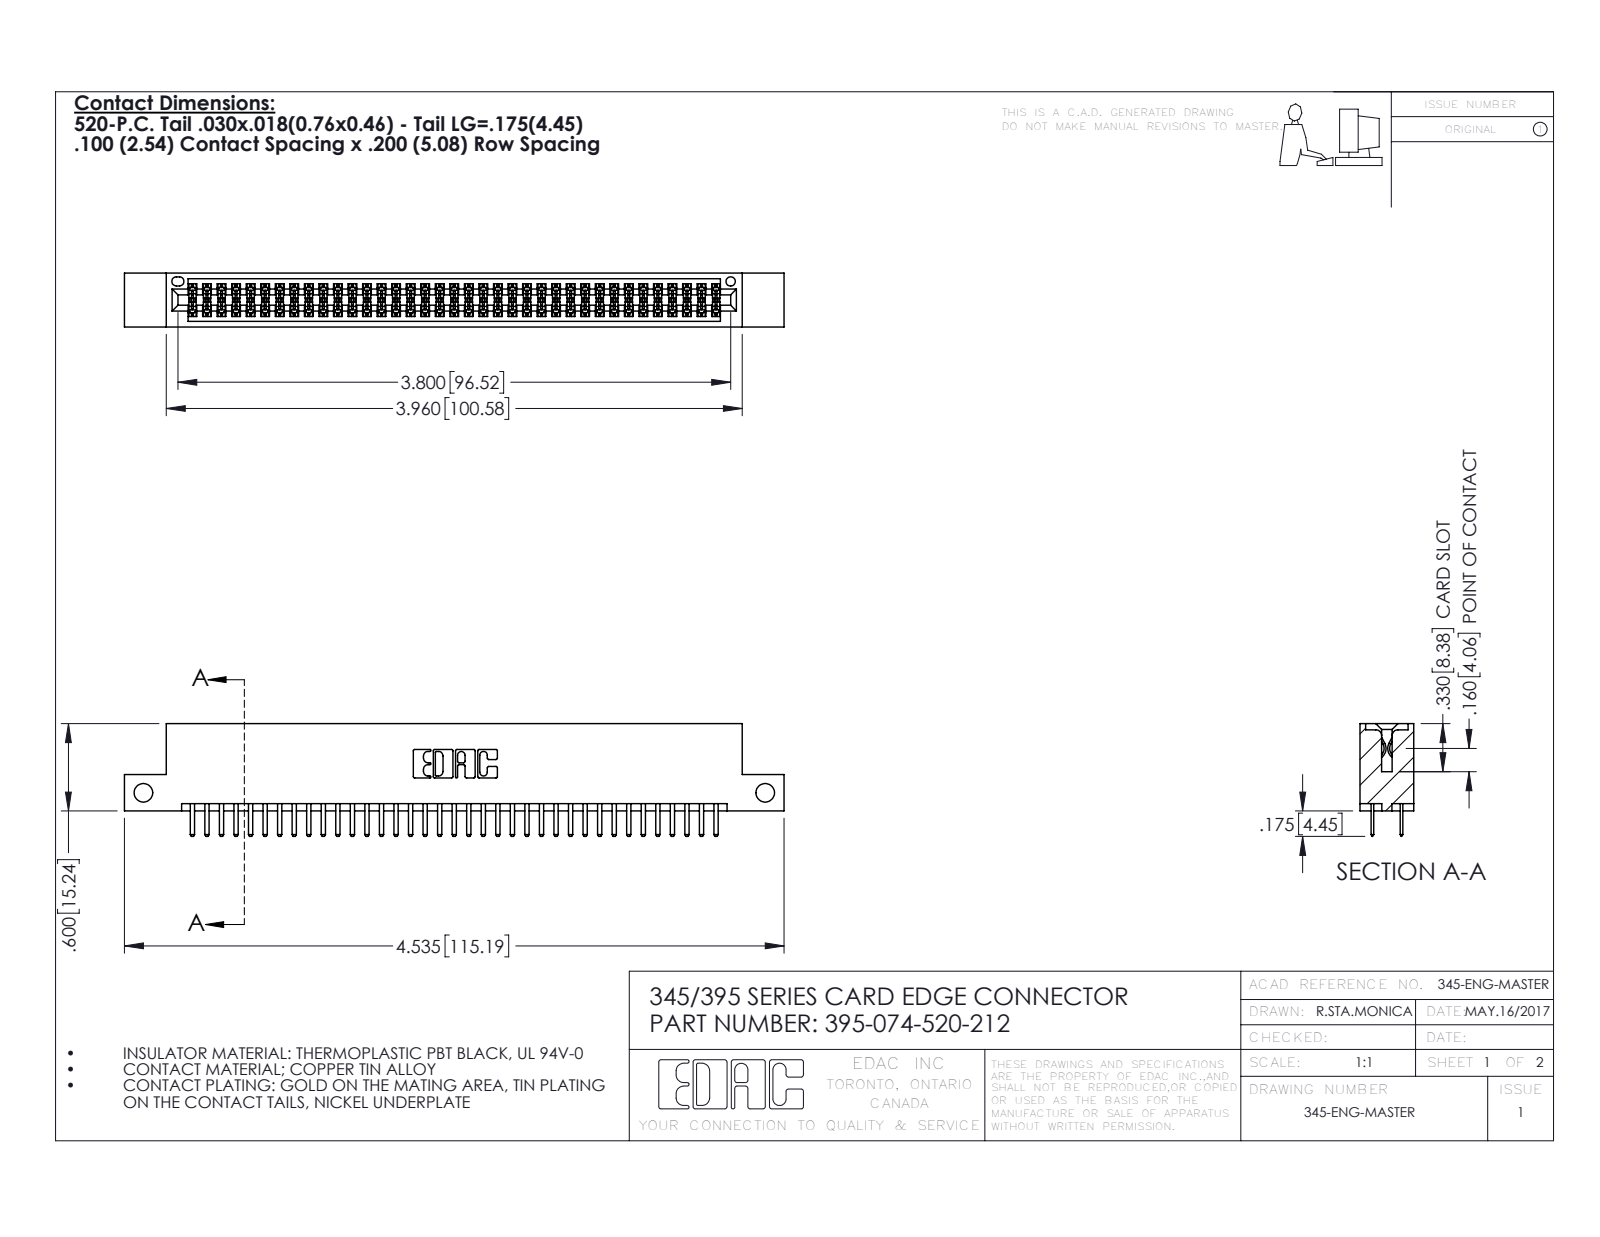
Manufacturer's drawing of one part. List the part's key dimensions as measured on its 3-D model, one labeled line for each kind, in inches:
Part name (STEP PRODUCT): 345-292-001_345-293-120; 345 Part_Flush Mounting Lugs - Side Mount; 395-074-520-212
STEP written by: SolidWorks 2016 (CONFIG_CONTROL_DESIGN)
Units: inches
Bodies: 75 solids, 4122 faces (2670 planar, 1452 cylindrical, 0 other)
Overall size (bounding box): 4.535 × 0.775 × 0.37
Volume: 0.673 in³ · Surface area: 24.79 in²
Round holes (diameter × count): ⌀0.128 ×2, ⌀0.064 ×1
Partial cylindrical surfaces — rounded edges, fillets, slot ends (radius × count): R0.006 ×111, R0.01 ×78, R0.01 ×22, R0.007 ×6, R0.031 ×6, R0.026 ×3, R0.014 ×2, R0.019 ×2
Main face-to-face distances: 0.298, 0.072, 0.2, 0.37, 0.098, 0.272, 0.025, 0.225, 0.022, 0.072
Hole centre spacings: 4.275
